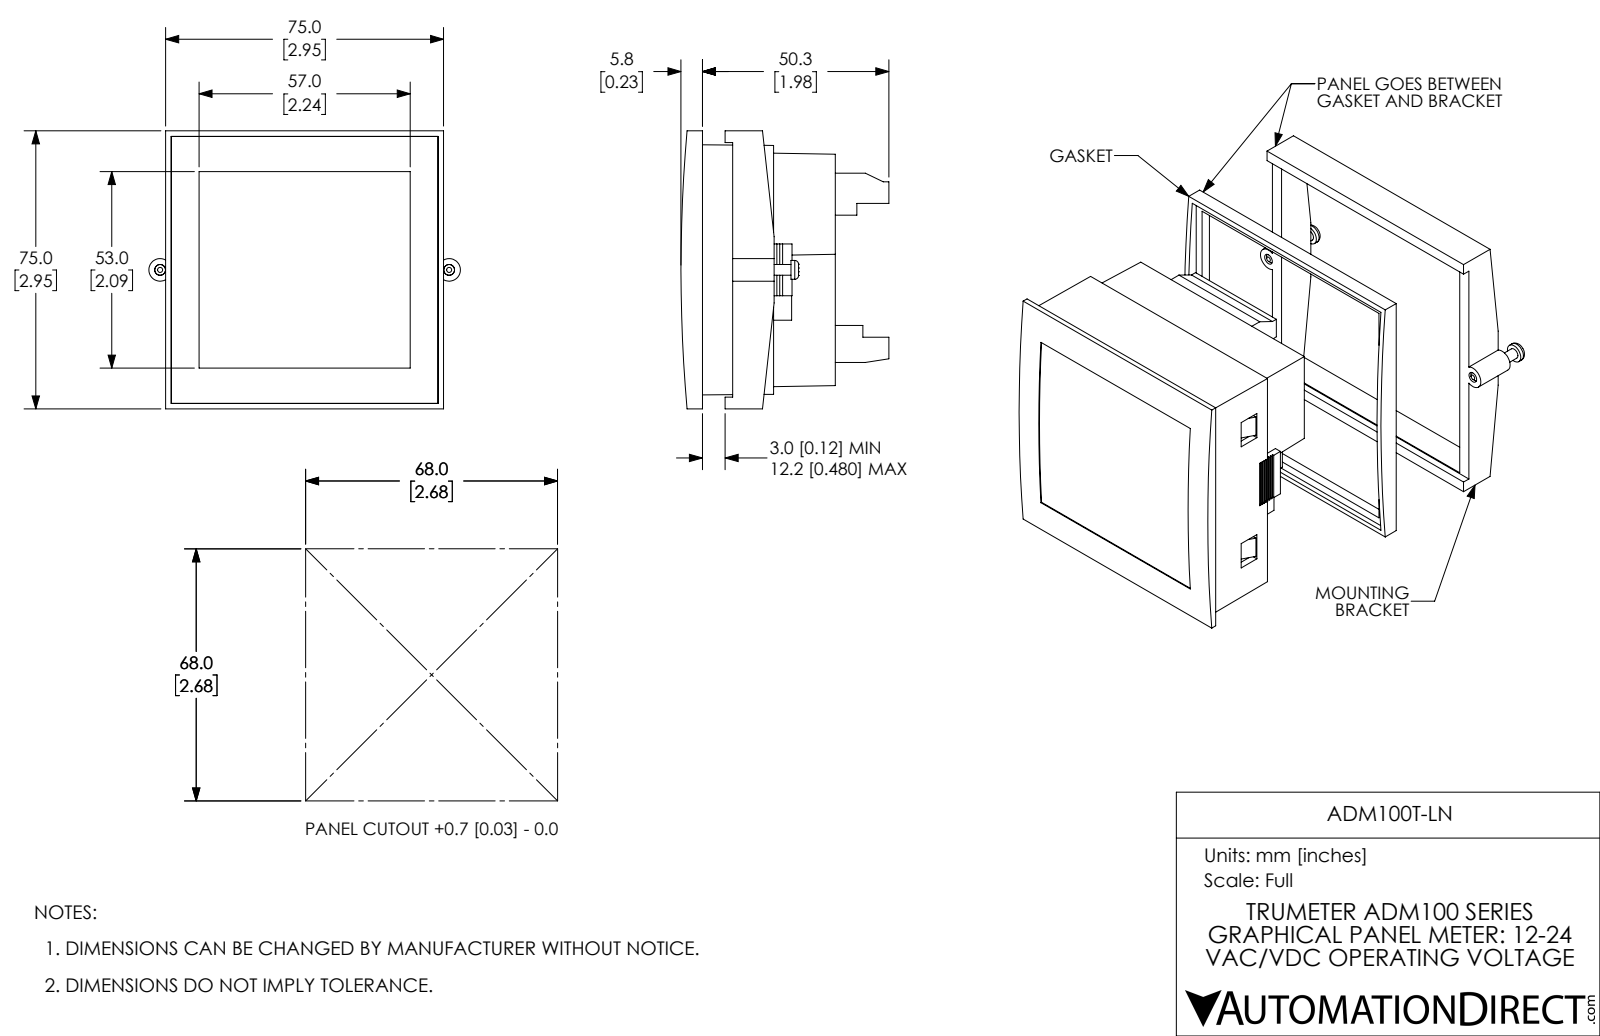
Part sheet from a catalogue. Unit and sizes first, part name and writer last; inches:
Units: inches
Overall size (bounding box): 3.311 × 2.953 × 2.209
Round holes (diameter × count): ⌀0.151 ×13, ⌀0.115 ×2
Round bosses / shafts (diameter × count): ⌀0.148 ×13, ⌀0.2 ×2, ⌀0.114 ×2
Partial cylindrical surfaces — rounded edges, fillets, slot ends (radius × count): R0.12 ×2, R17.037 ×2
Main face-to-face distances: 0.075, 0.305, 0.236, 2.717, 2.657, 0.089, 0.148, 2.805, 2.583, 1.142
Hole centre spacings: 1.653, 0.2, 1.677, 0.4, 1.724, 0.6, 1.792, 0.8
Volume: 9.565 in³ · Surface area: 90.64 in²
Bodies: 23 solids, 419 faces (335 planar, 76 cylindrical, 8 other)
Part name (STEP PRODUCT): ADM100T-LN
STEP written by: SolidWorks 2021 (CONFIG_CONTROL_DESIGN)
